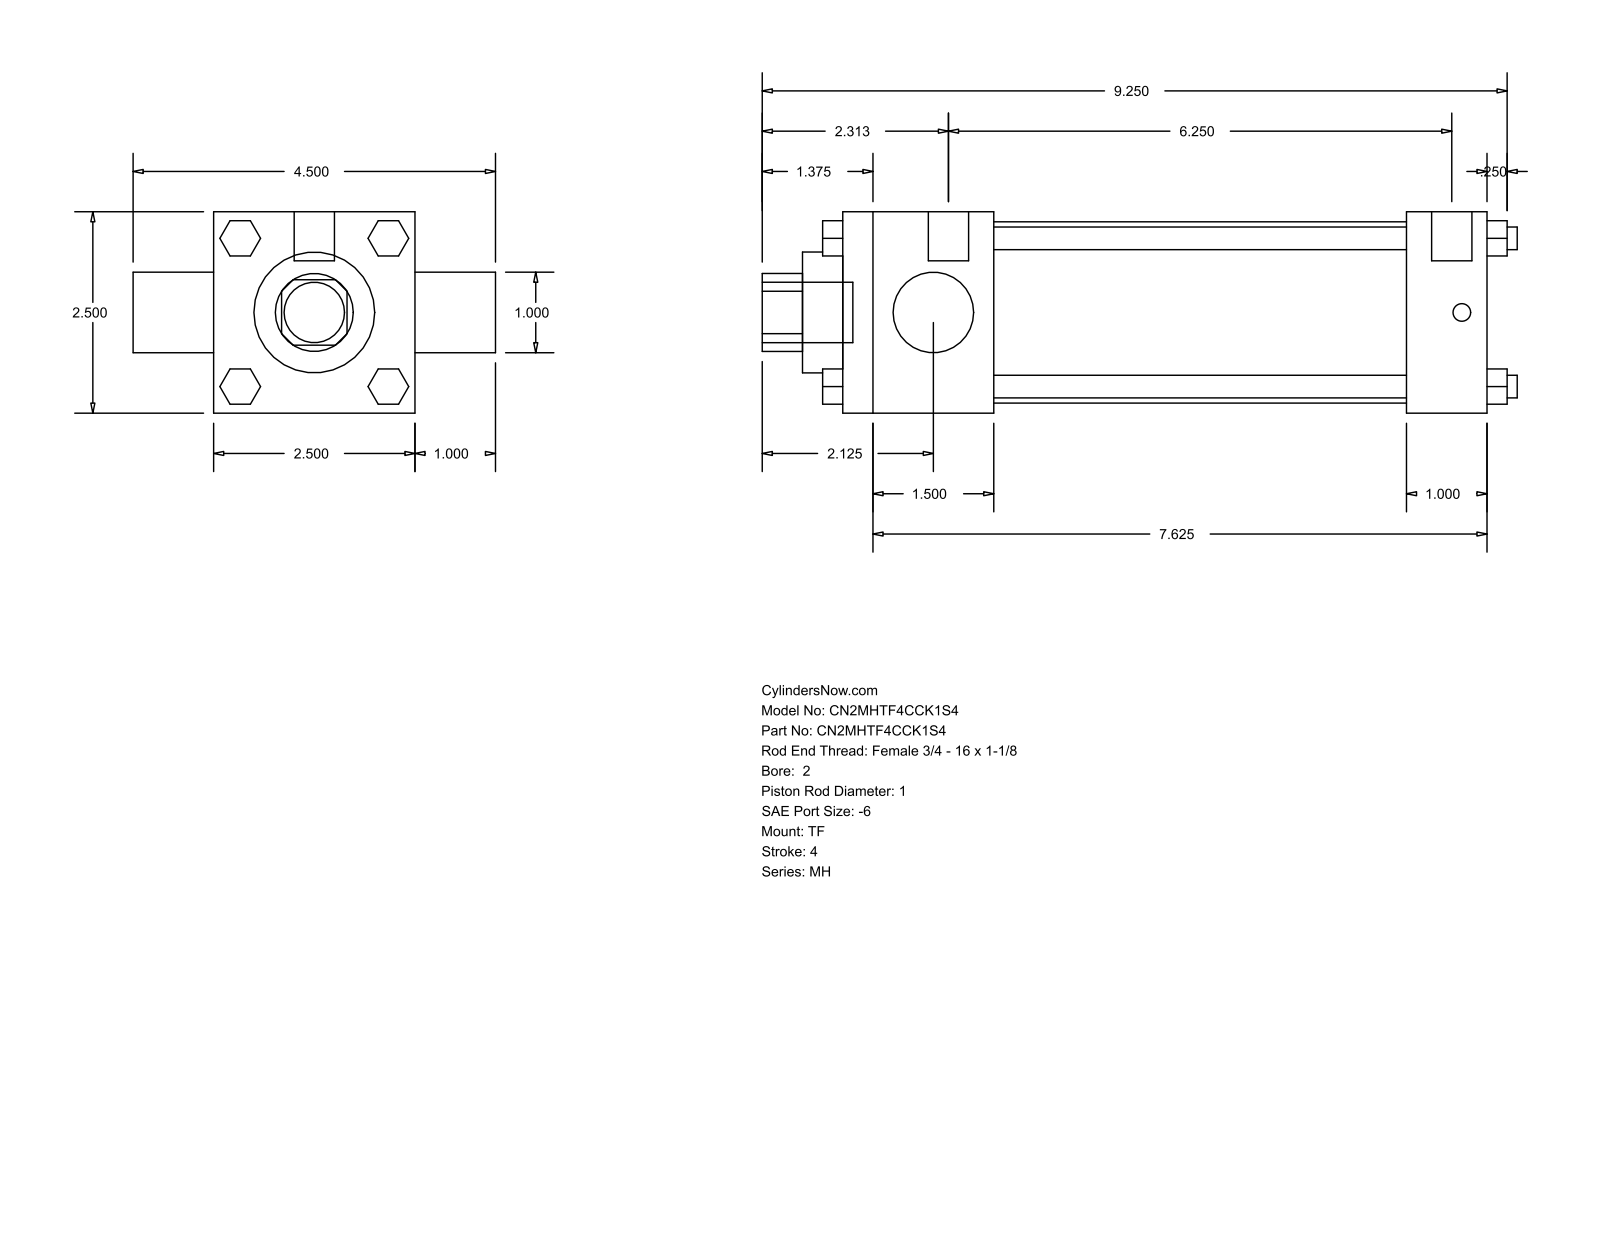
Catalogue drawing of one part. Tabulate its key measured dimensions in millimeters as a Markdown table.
| quantity | value |
| --- | --- |
| part name | MH_TF__0200_1 |
| STEP written by | GSSL Pune (CONFIG_CONTROL_DESIGN) |
| units | millimeters |
| bodies | 0 solids, 120 faces (92 planar, 28 cylindrical, 0 other) |
| overall size | 238.12 × 114.3 × 63.5 |
| round holes (diameter × count) | 25.4 × 2, 38.1 × 1, 57.15 × 1 |
| round bosses / shafts (diameter × count) | 7.14 × 4, 5.56 × 3, 12.7 × 2, 19.05 × 1 |
| partial cylindrical surfaces (radius × count) | 12.29 × 1 |
| main face-to-face distances | 63.5, 203.2, 25.4, 47.63, 177.8, 130.17, 155.57, 88.9, 215.9, 6.35 |
